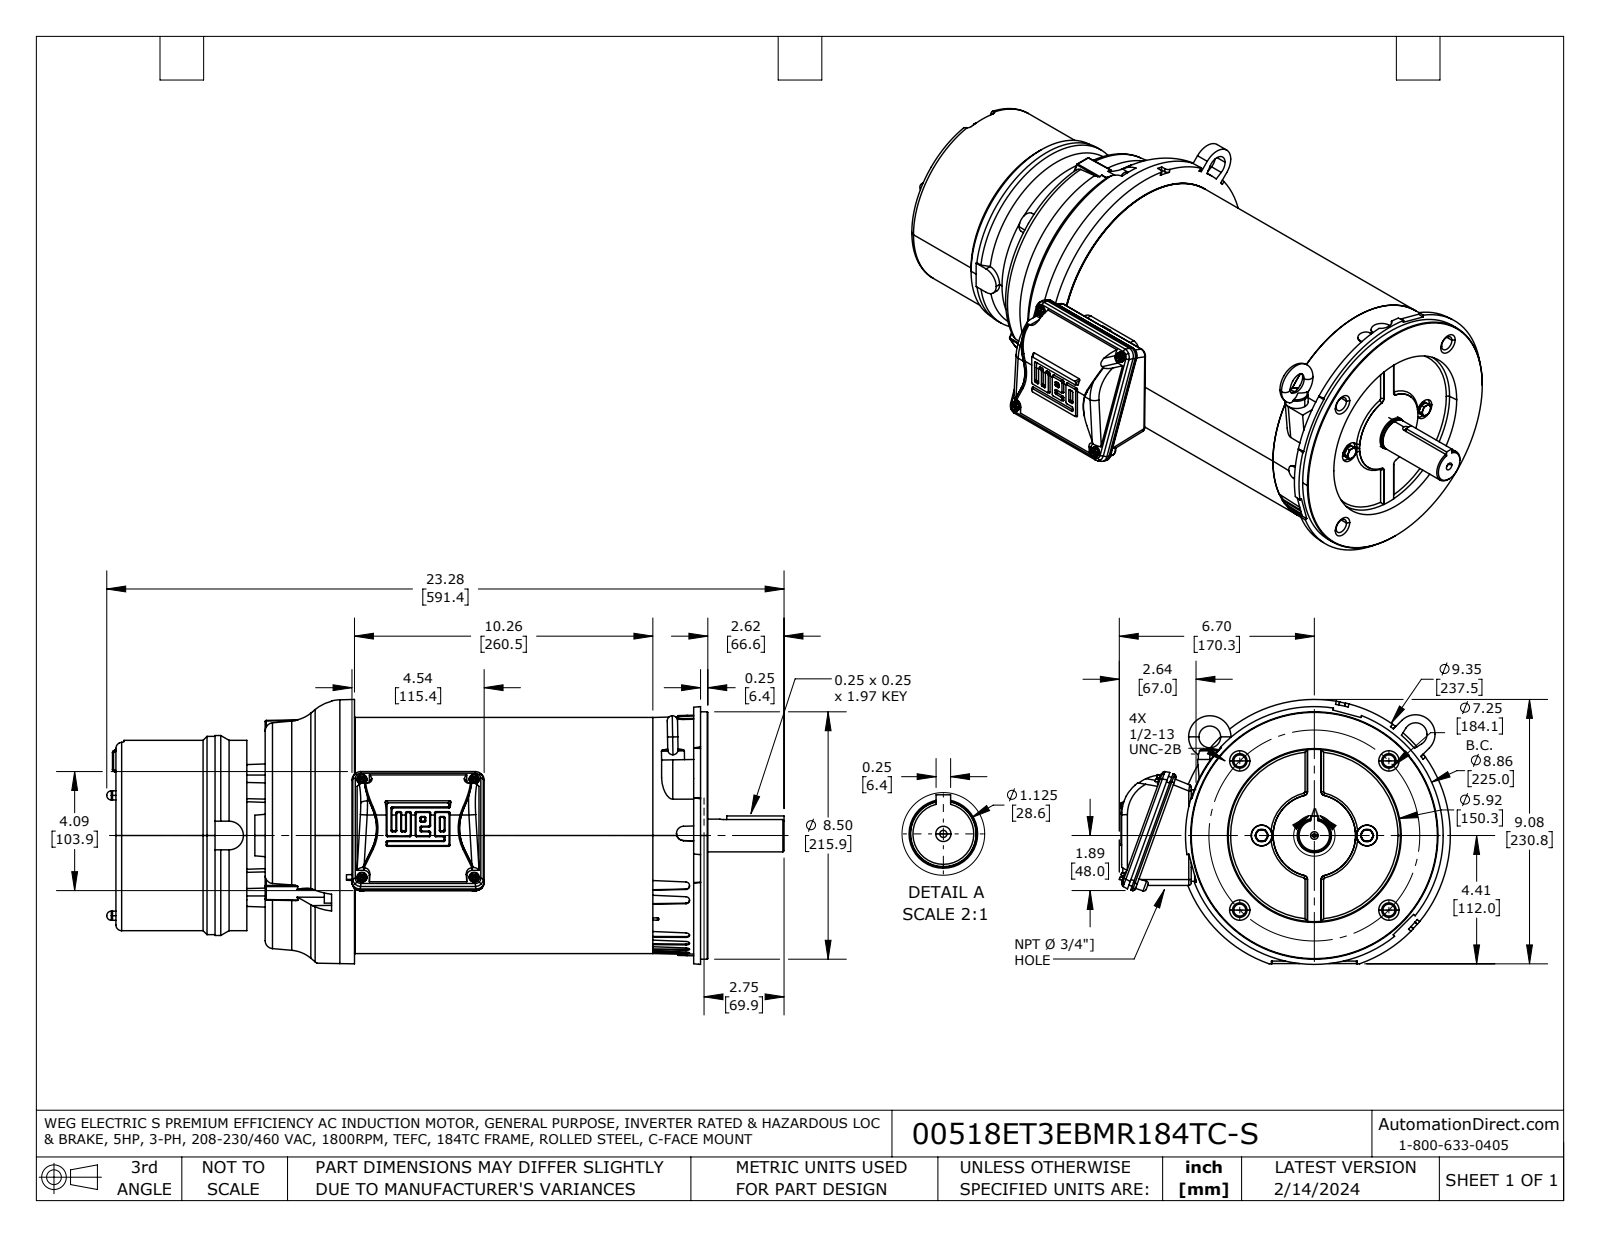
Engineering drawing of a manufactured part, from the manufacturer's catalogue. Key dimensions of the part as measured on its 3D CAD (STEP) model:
Part name (STEP PRODUCT): 00518ET3EBMR184TC-S
STEP written by: SolidWorks 2021 (AUTOMOTIVE_DESIGN)
Units: inches
Bodies: 20 solids, 1197 faces (455 planar, 311 cylindrical, 431 other)
Overall size (bounding box): 23.281 × 11.38 × 9.104
Volume: 993.1 in³ · Surface area: 1 105 in²
Round holes (diameter × count): ⌀0.413 ×4, ⌀0.5 ×4, ⌀0.252 ×2, ⌀0.124 ×1
Round bosses / shafts (diameter × count): ⌀0.348 ×4, ⌀0.375 ×3, ⌀0.315 ×3, ⌀0.25 ×3, ⌀0.433 ×2, ⌀0.35 ×2, ⌀8.5 ×1, ⌀8.114 ×1
Partial cylindrical surfaces — rounded edges, fillets, slot ends (radius × count): R0.047 ×40, R0.126 ×22, R0.039 ×14, R0.087 ×12, R0.118 ×8, R0.205 ×8, R0.276 ×8, R0.02 ×4
Main face-to-face distances: 10.236, 3.72, 13.957, 4.5, 8.22, 18.457, 20.346, 15.846, 12.126, 1.89
Hole centre spacings: 5.07, 1.811, 2.671, 2.672, 3.625, 3.625, 5.126, 5.127
